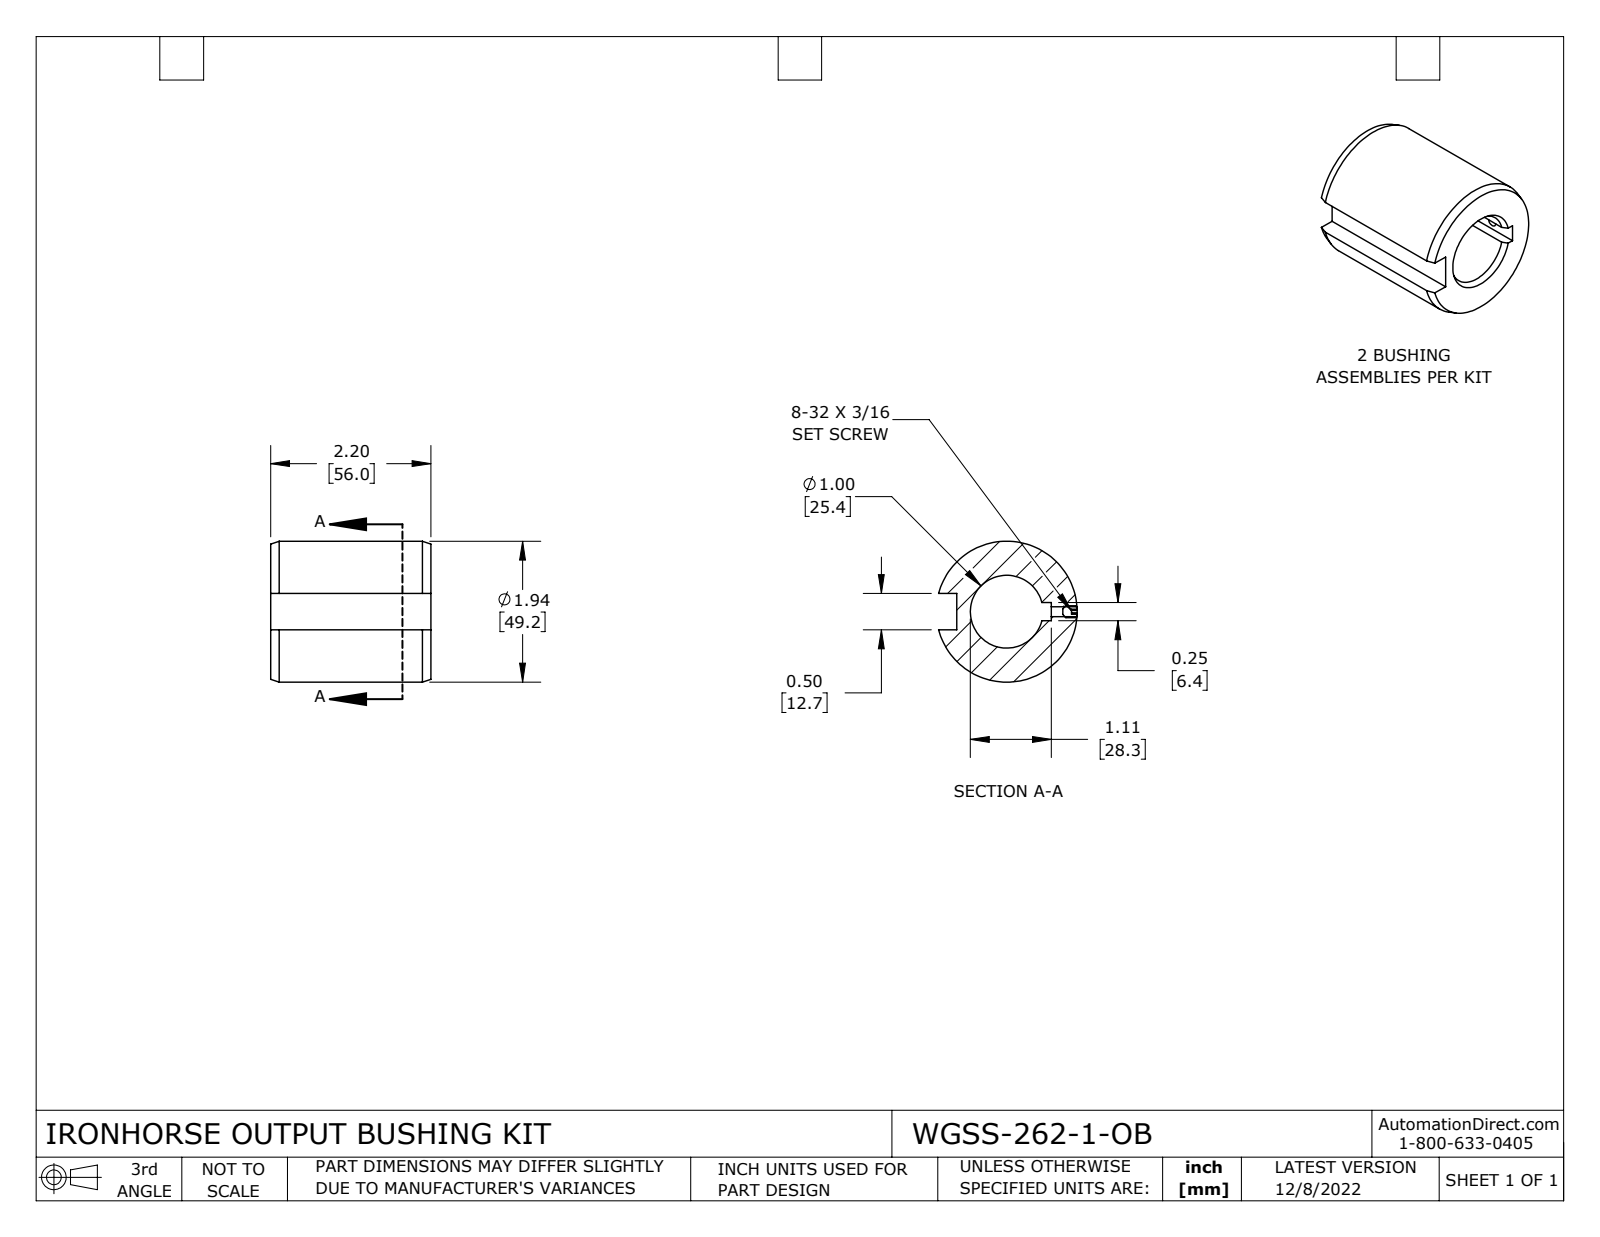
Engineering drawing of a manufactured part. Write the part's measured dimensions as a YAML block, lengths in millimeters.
part_name: "WGSS-262-1-OB"
step_written_by: "SolidWorks 2021 (CONFIG_CONTROL_DESIGN)"
units: millimeters
bodies: {solids: 2, faces: 41, planar: 17, cylindrical: 10, other: 14}
overall_size: [56, 49.21, 48.38]
volume: 71530
surface_area: 16561
round_holes:
  - {diameter: 3.45, count: 1}
  - {diameter: 25.4, count: 1}
round_bosses_or_shafts:
  - {diameter: 49.21, count: 1}
  - {diameter: 4.16, count: 1}
face_to_face_distances: [56, 3.18, 9.52, 12.7, 33.02, 6.34, 1.5, 4.01, 37.03, 5]
